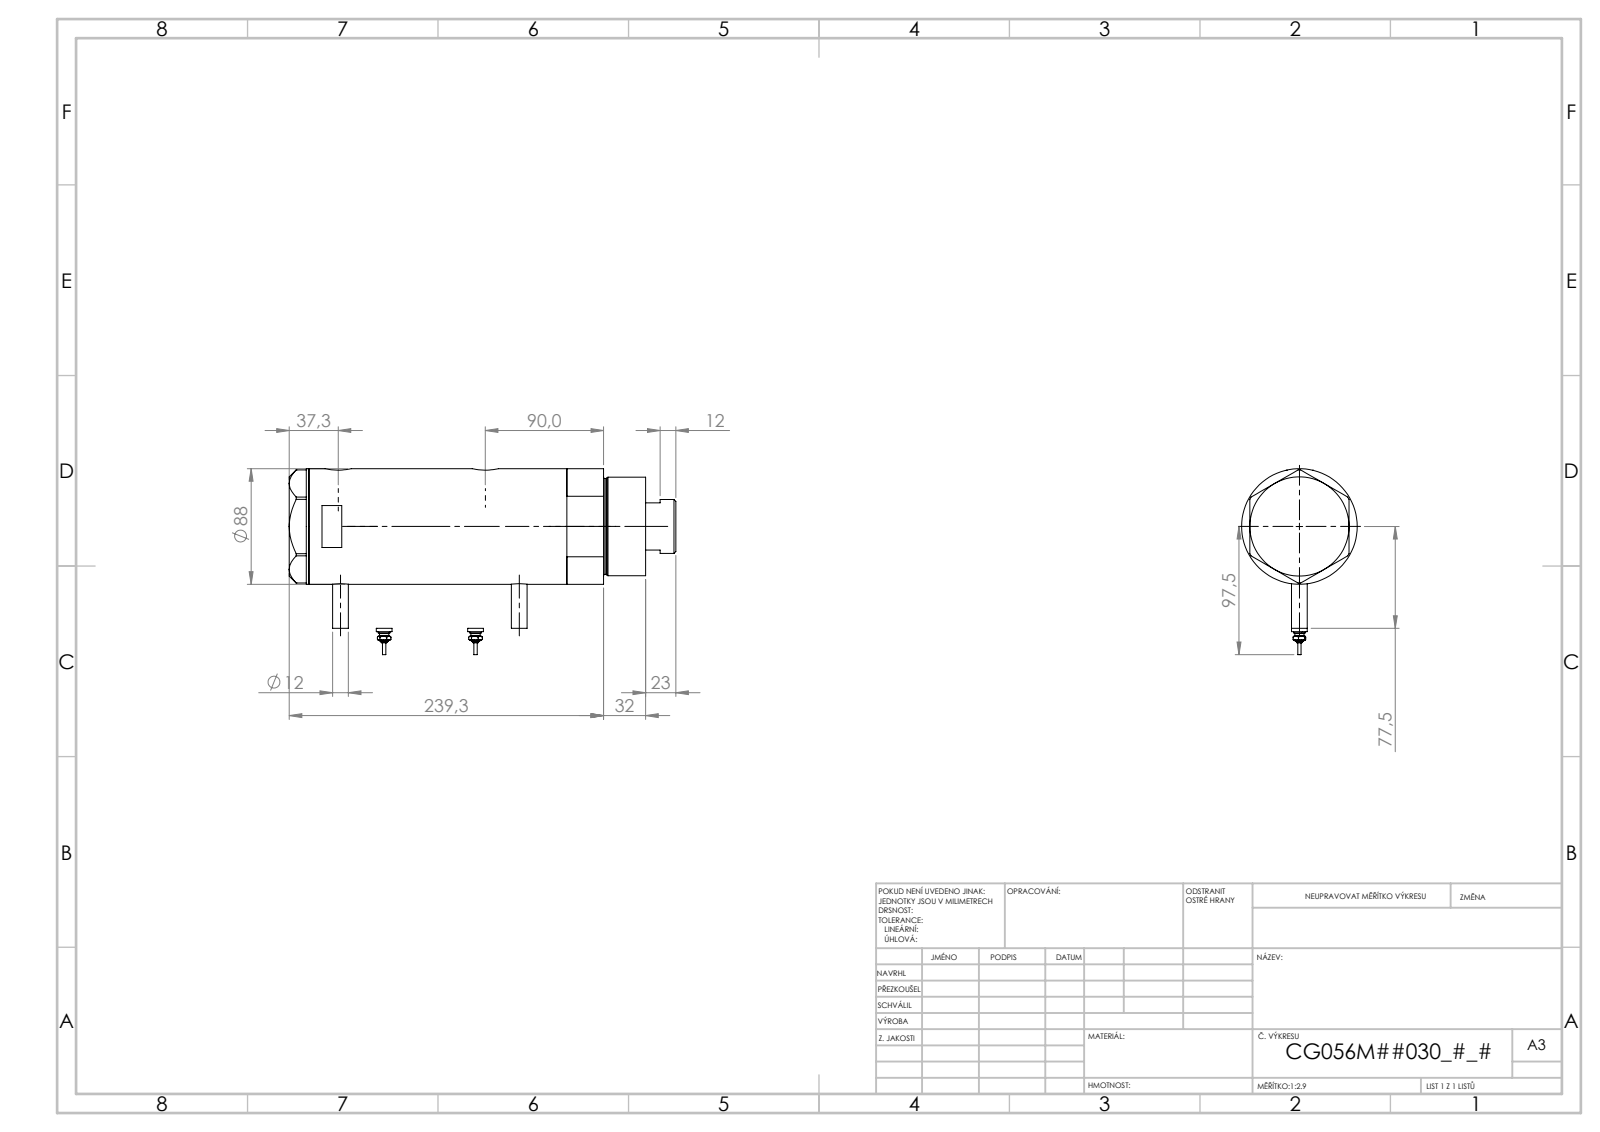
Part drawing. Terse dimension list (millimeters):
name: V270CG_SWITCH; V270CG_FRONT; V270CG_MIDDLE; V270CG_VC (+1 more)
written by: SolidWorks 2019 (CONFIG_CONTROL_DESIGN)
unit: mm
bodies: 6 solids, 232 faces (81 planar, 77 cylindrical, 74 other)
size: 254.47 × 120.3 × 88
volume: 1 315 000 mm³; area: 199 737 mm²
holes: 2× ⌀5, 2× ⌀12.5, 2× ⌀13.16, 2× ⌀20, 1× ⌀14.5, 1× ⌀42, 1× ⌀43.5, 1× ⌀56, 1× ⌀60, 1× ⌀80
bosses: 2× ⌀12, 2× ⌀9, 2× ⌀7, 2× ⌀4.34, 2× ⌀2.4, 1× ⌀88, 1× ⌀75, 1× ⌀73
face distances: 104.4, 26, 78.4, 15, 41, 119.4, 216.47, 231.47, 190.47, 112.07
hole spacings: 1.7, 25.8, 80.3, 82, 106.1, 107.8
